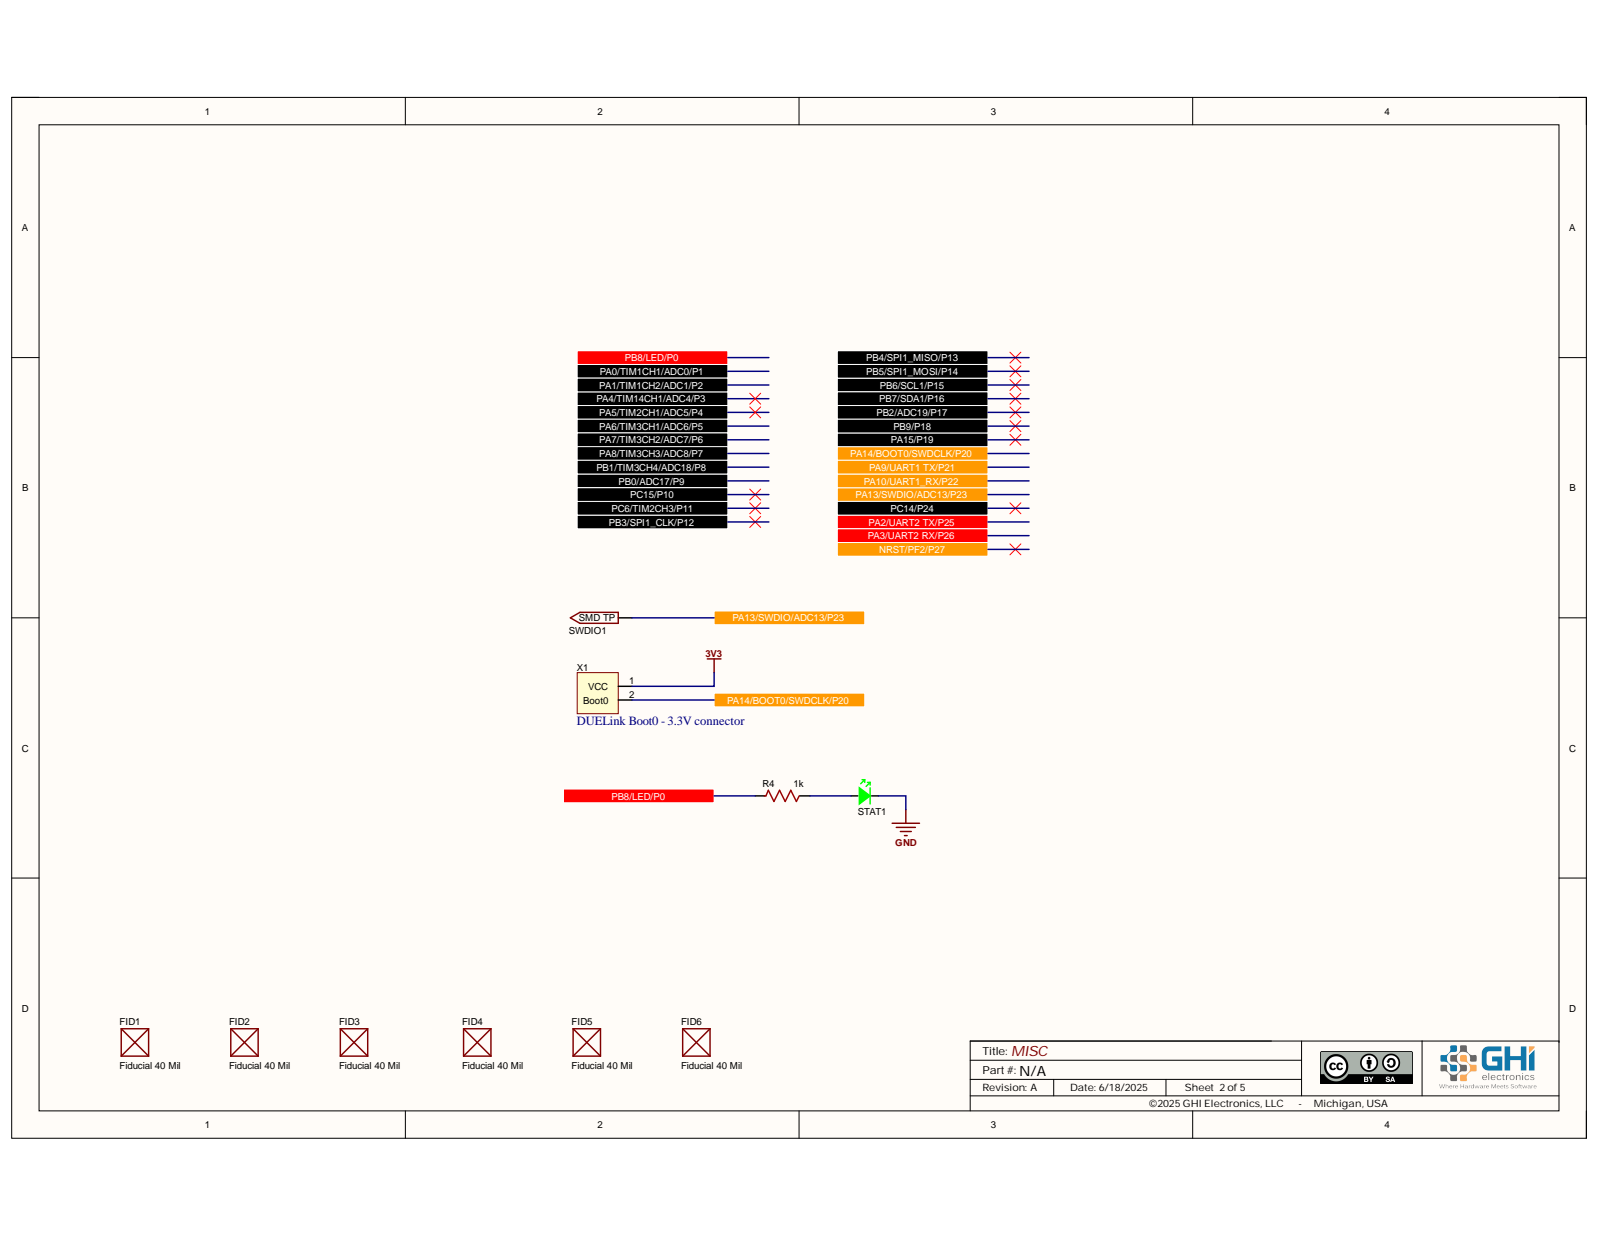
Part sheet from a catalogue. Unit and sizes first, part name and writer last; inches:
Units: inches
Overall size (bounding box): 1.457 × 1.063 × 0.701
Round holes (diameter × count): ⌀0.04 ×18, ⌀0.039 ×16, ⌀0.118 ×4, ⌀0.04 ×2, ⌀0.063 ×2
Round bosses / shafts (diameter × count): ⌀0.059 ×2, ⌀0.031 ×2, ⌀0.197 ×1, ⌀0.142 ×1
Partial cylindrical surfaces — rounded edges, fillets, slot ends (radius × count): R0.006 ×47, R0.005 ×35, R0.004 ×28, R0.008 ×20, R0.013 ×8, R0.031 ×8, R0.008 ×5, R0.007 ×4
Main face-to-face distances: 0.262, 0.27, 0.1, 0.217, 0.045, 0.224, 0.7, 0.2, 0.025, 0.037
Hole centre spacings: 0.1, 0.707, 0.2, 0.3, 0.7, 0.4, 0.728, 0.5
Volume: 0.134 in³ · Surface area: 11.14 in²
Bodies: 205 solids, 5773 faces (3881 planar, 1170 cylindrical, 722 other)
Part name (STEP PRODUCT): PCB; Board; STAT1; 0603 LED Green (+5 more)
STEP written by: Open CASCADE 7.5 (AUTOMOTIVE_DESIGN)
